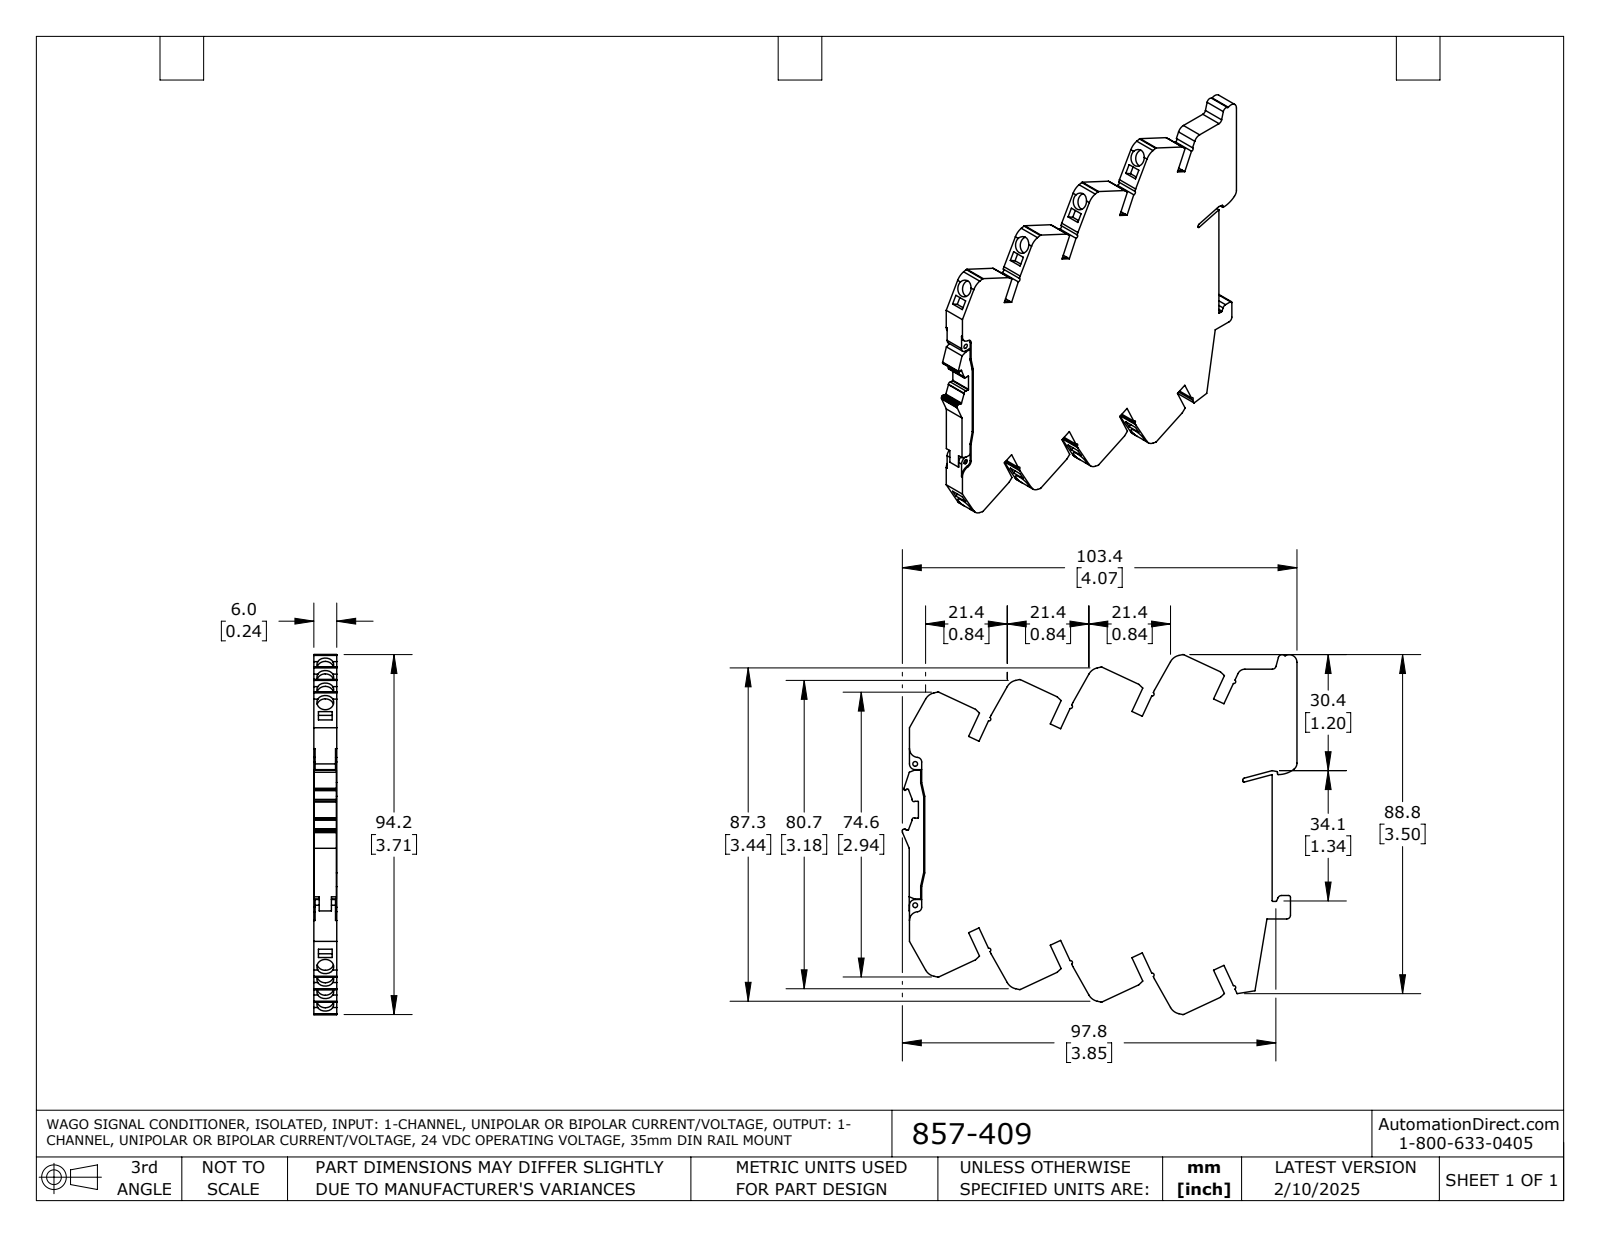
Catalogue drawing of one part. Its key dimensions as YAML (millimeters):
part_name: "857-409"
step_written_by: "SolidWorks 2021 (AUTOMOTIVE_DESIGN)"
units: millimeters
bodies: {solids: 1, faces: 317, planar: 219, cylindrical: 98, other: 0}
overall_size: [103.4, 94.3, 6]
volume: 43930
surface_area: 19260
round_holes:
  - {diameter: 4.4, count: 8}
  - {diameter: 1.2, count: 2}
partial_cylinders:
  - {radius: 0.5, count: 12}
  - {radius: 0.2, count: 11}
  - {radius: 0.4, count: 8}
  - {radius: 3.4, count: 8}
  - {radius: 1, count: 4}
  - {radius: 0.3, count: 3}
  - {radius: 2, count: 3}
  - {radius: 0.5, count: 2}
face_to_face_distances: [6, 18, 17, 12, 5.9, 12, 3, 24, 36, 6.5]
hole_center_spacings: [13.4, 13.3, 26.7, 26.7, 26.7, 37, 40, 40.1]
